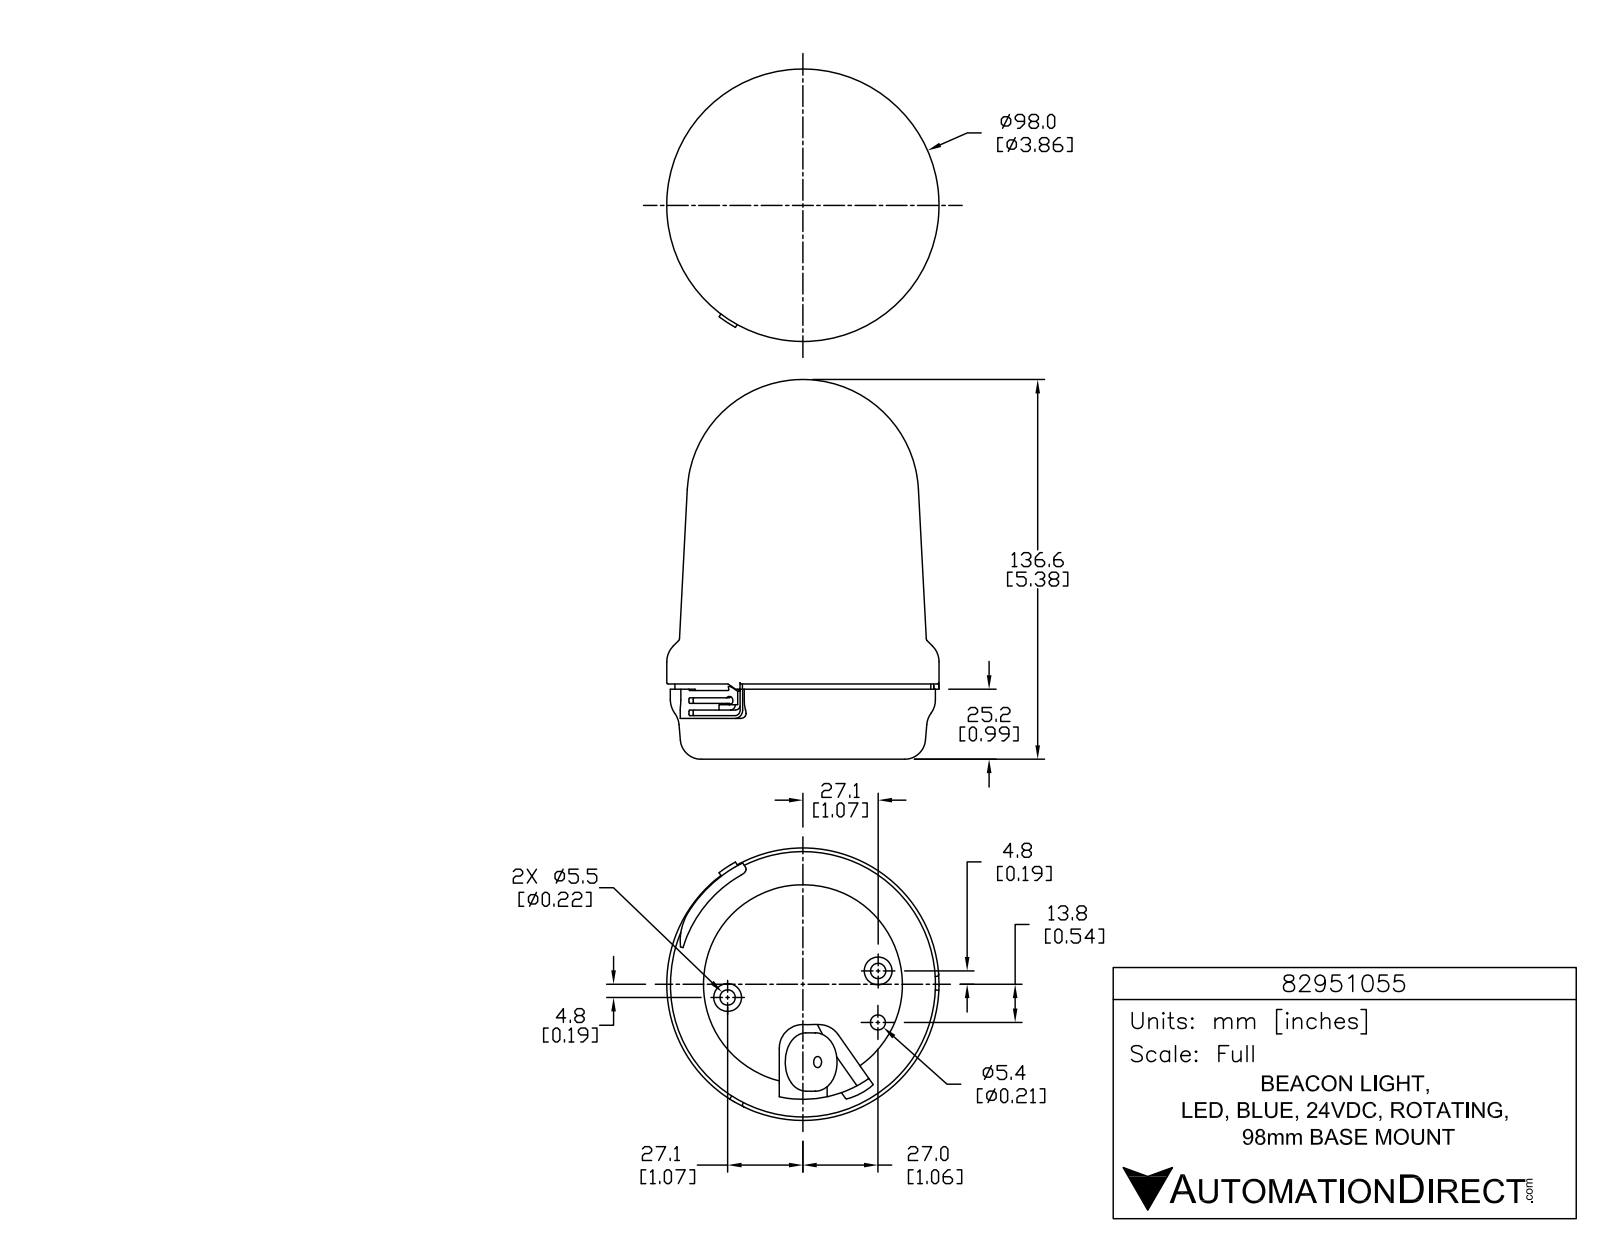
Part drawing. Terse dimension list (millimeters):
name: 82951055
written by: SolidWorks 2015 (AUTOMOTIVE_DESIGN)
unit: mm
bodies: 1 solid, 872 faces (566 planar, 204 cylindrical, 102 other)
size: 136.6 × 98 × 98
volume: 732 300 mm³; area: 47 520 mm²
holes: 3× ⌀1.5, 2× ⌀5.5, 1× ⌀4, 1× ⌀5.4, 1× ⌀71.6
bosses: 3× ⌀8.6, 3× ⌀2.1, 2× ⌀10, 1× ⌀98, 1× ⌀95.4, 1× ⌀92.1, 1× ⌀21
rounds: 9× R0.1, 6× R0.1, 6× R0.3, 6× R0.3, 6× R0.3, 6× R5, 5× R0.5, 4× R1
face distances: 26.5, 24.7, 1.9, 0.5, 25.2, 27.1, 6, 14.7, 14.2, 10.5
hole spacings: 27.5, 18.5, 30.3, 54.8, 55
